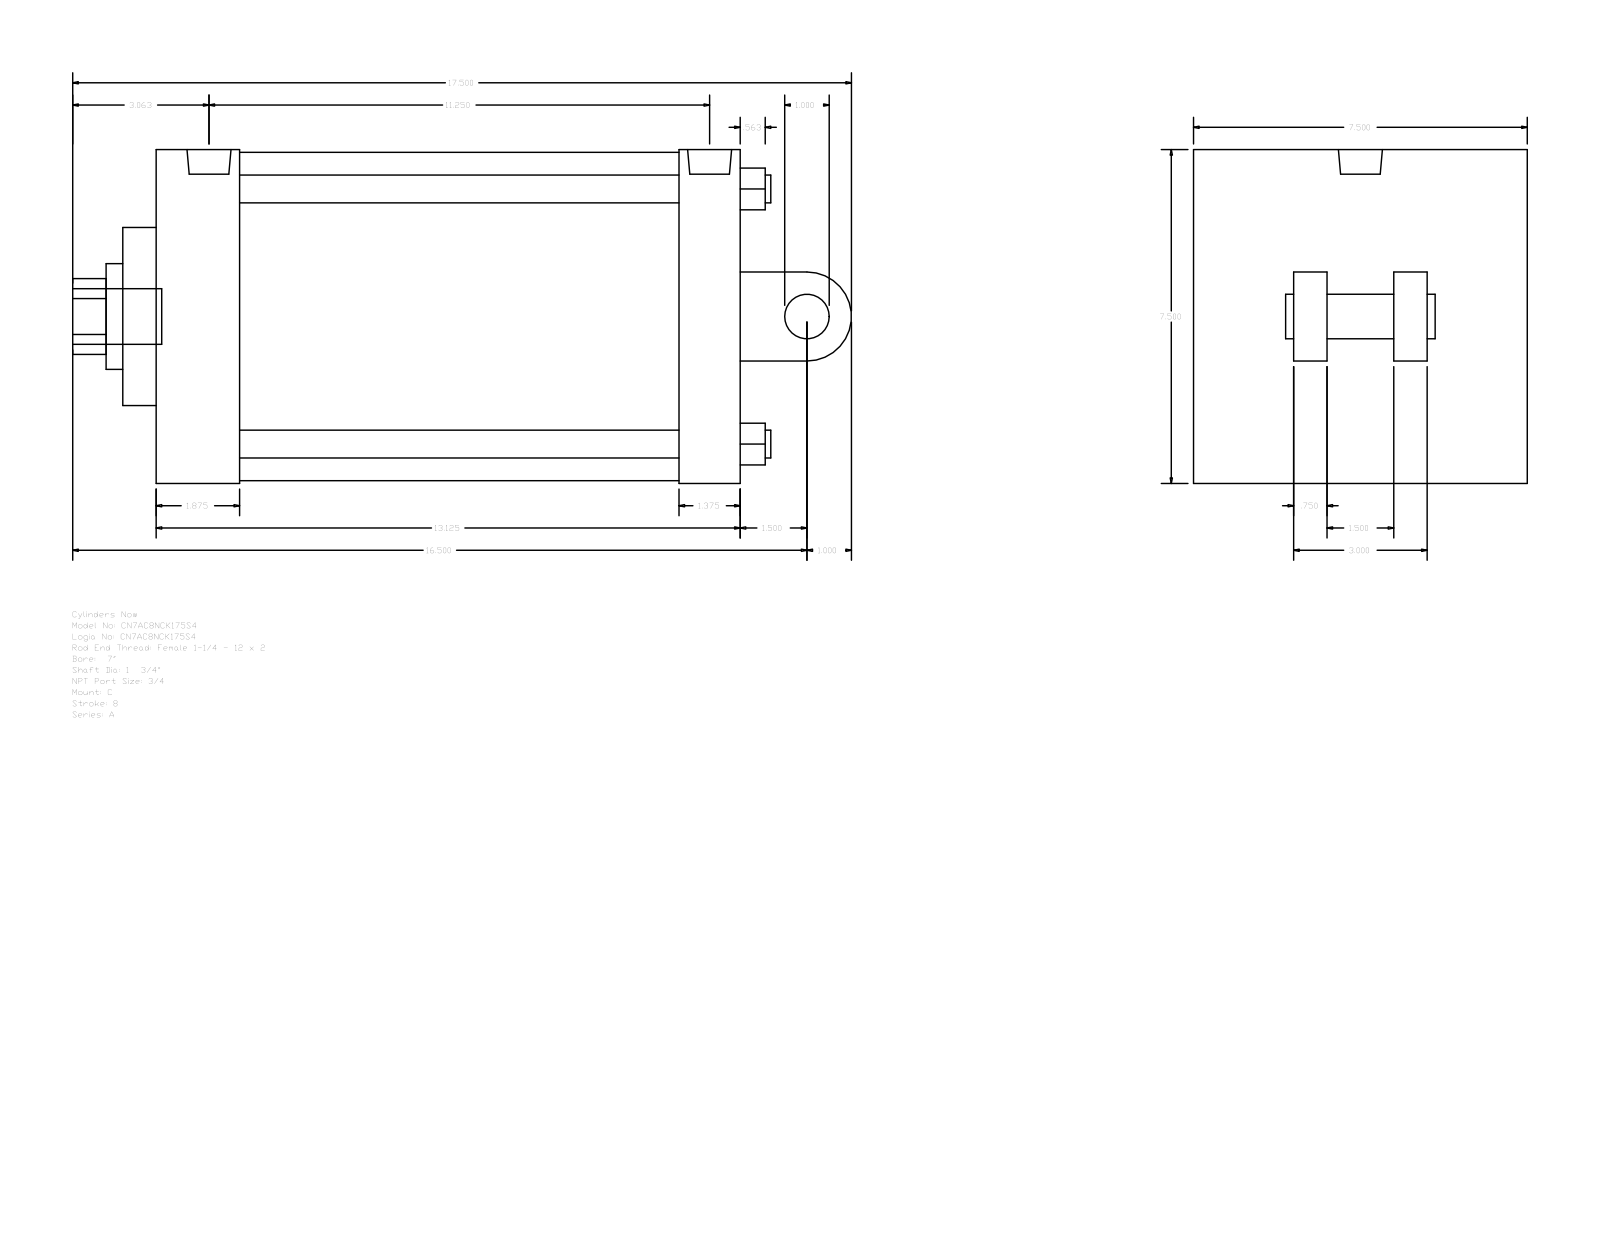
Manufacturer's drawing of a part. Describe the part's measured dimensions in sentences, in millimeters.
The part is named "A_C__0700_1.75". Its 3-D file was written by "GSSL Pune (CONFIG_CONTROL_DESIGN)". It is 0 solids with 104 faces: 75 planar, 29 cylindrical and 0 other. Overall it measures 444.5 by 190.5 by 190.5 millimeters. Round holes: 4 of diameter 15.88, 2 of diameter 15.08, 1 of diameter 25.12, 1 of diameter 44.45, 1 of diameter 60.33, 1 of diameter 187.32. Round bosses or shafts: 2 of diameter 15.08, 1 of diameter 31.75, 1 of diameter 25.4, 1 of diameter 25.12. Partial cylindrical surfaces (rounded edges, fillets, slot ends): 1 of radius 21.63, 1 of radius 25.4. The main face-to-face distances are 190.5, 333.38, 19.05, 76.2, 57.15, 44.45, 47.63, 285.75, 298.45, 250.82. The hole center spacings are 102.91, 145.54, 205.82, 5.56.
